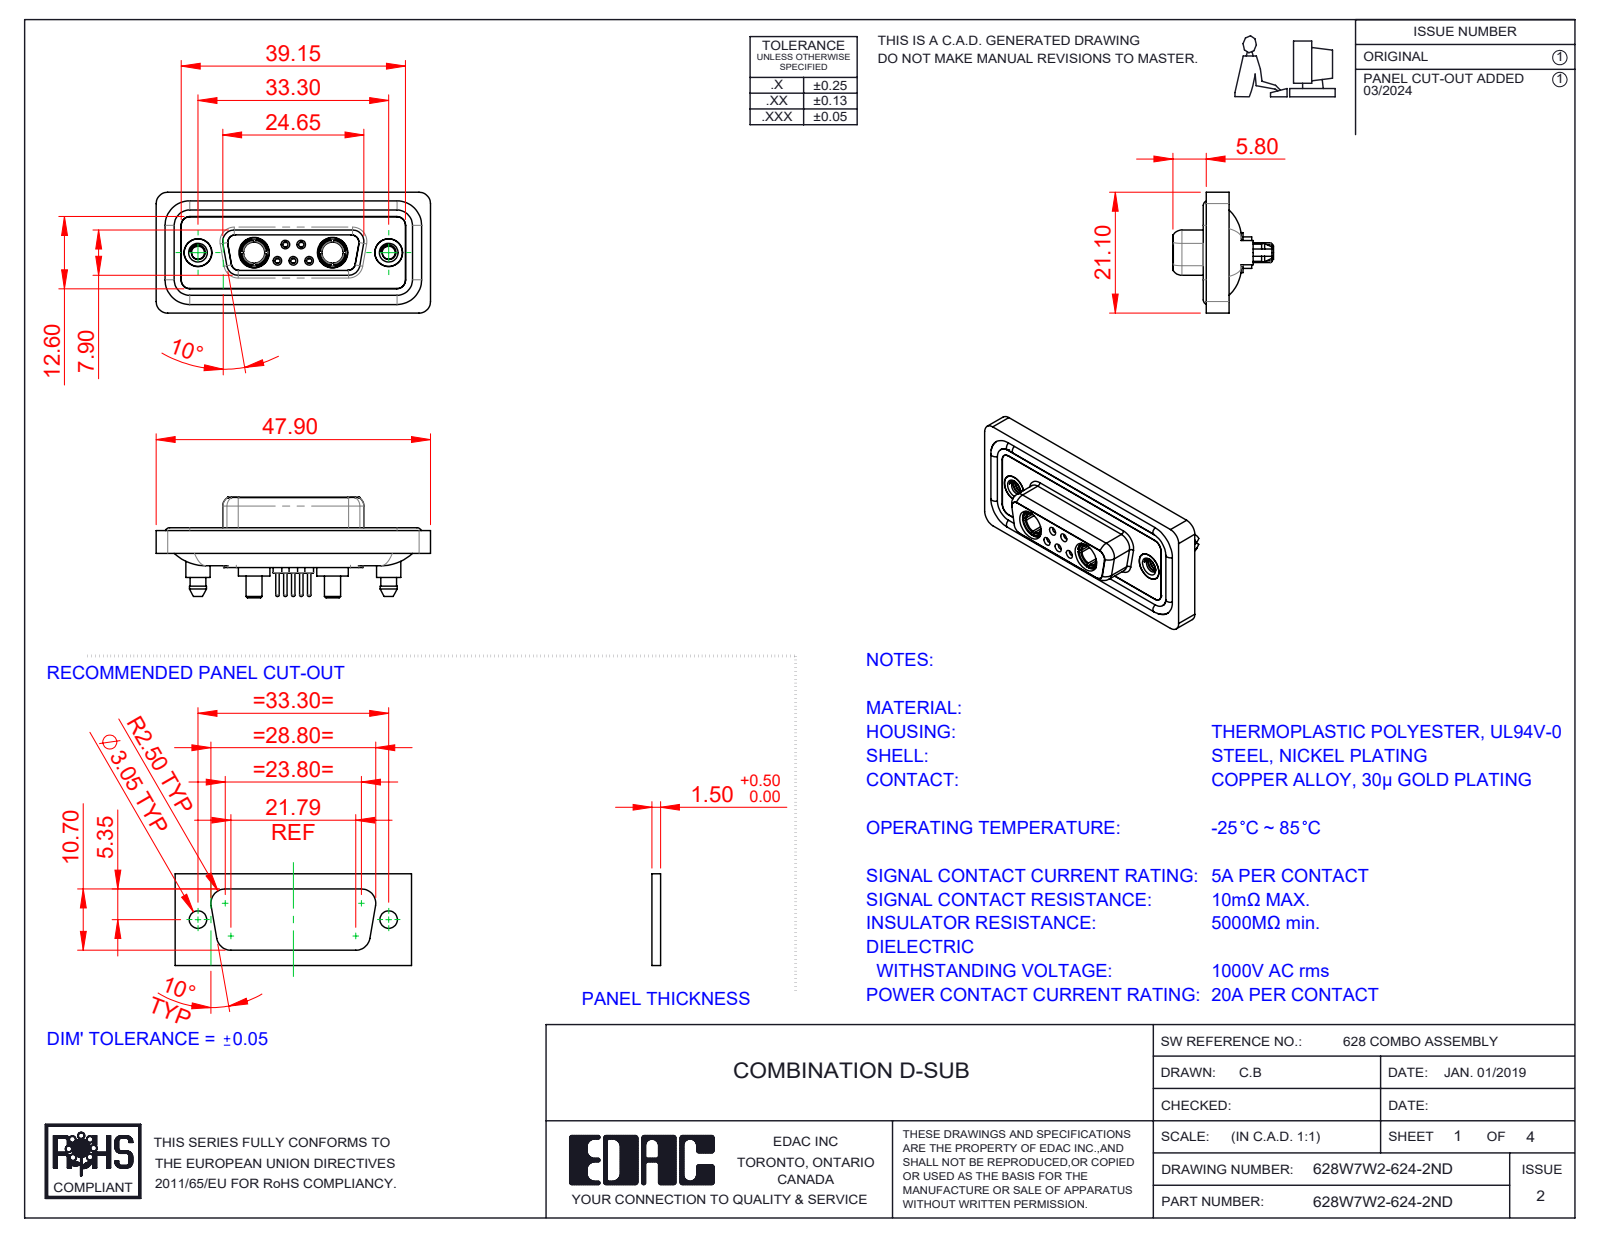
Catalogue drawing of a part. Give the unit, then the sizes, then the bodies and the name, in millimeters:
Units: millimetres
Overall size (bounding box): 47.9 × 21.1 × 17.55
Round holes (diameter × count): ⌀0.9 ×5, ⌀1.1 ×5, ⌀1.5 ×5, ⌀2 ×5, ⌀4.85 ×4, ⌀1.6 ×3, ⌀1.7 ×2, ⌀2.26 ×2, ⌀3.7 ×2, ⌀4 ×2, ⌀4.05 ×2, ⌀5 ×2
Round bosses / shafts (diameter × count): ⌀1.6 ×6, ⌀2.2 ×5, ⌀0.6 ×5, ⌀5.5 ×2, ⌀5.4 ×2, ⌀5.2 ×2, ⌀4.96 ×2, ⌀4.95 ×2
Partial cylindrical surfaces — rounded edges, fillets, slot ends (radius × count): R1.5 ×24, R2 ×20, R1.35 ×12, R1.6 ×10, R0.25 ×4, R0.5 ×4, R0.6 ×4, R0.65 ×4
Main face-to-face distances: 0.4, 1.8, 1.6, 0.5, 2.9, 1.1, 7.45, 5.65, 6.6, 7.05
Hole centre spacings: 3.16, 2.77, 9.8, 23.5, 4.31, 4.33, 5.03, 5.04
Volume: 6 212 mm³ · Surface area: 10 224 mm²
Bodies: 16 solids, 875 faces (254 planar, 377 cylindrical, 244 other)
Part name (STEP PRODUCT): 628Combo Contact Row 2_24; 628Combo Shell Rear_15 Contacts; 628Combo Shell Front_15 Contacts; 628Combo Waterproof Housing_15 Contacts (+5 more)
STEP written by: SolidWorks 2023 (CONFIG_CONTROL_DESIGN)
